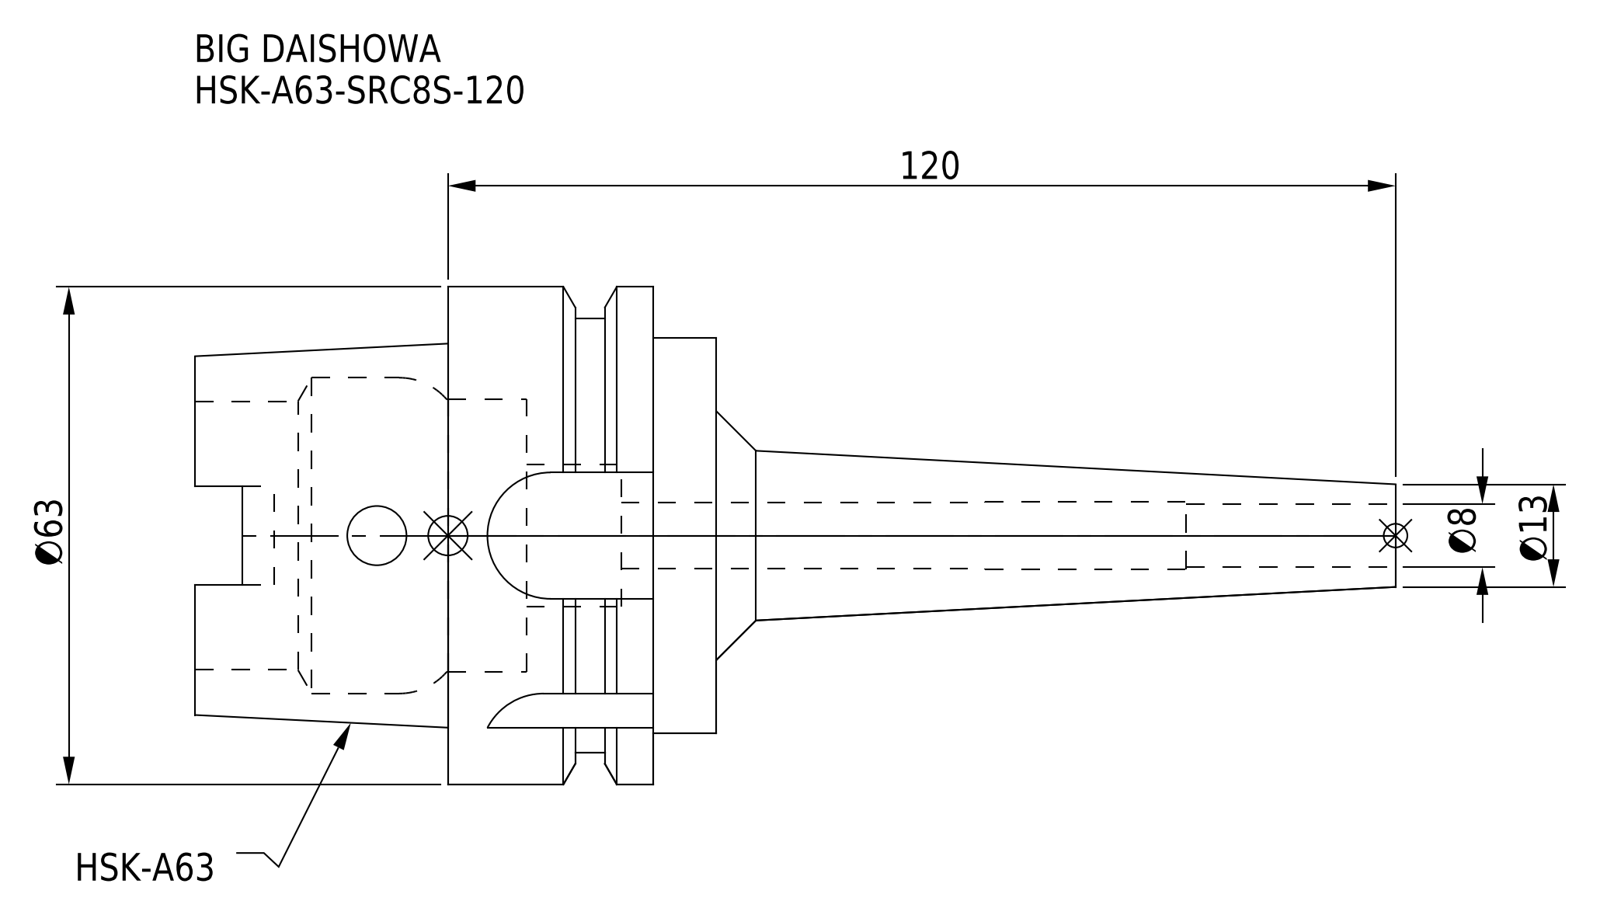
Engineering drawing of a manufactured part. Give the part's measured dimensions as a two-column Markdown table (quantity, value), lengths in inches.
| quantity | value |
| --- | --- |
| part name | HSK-A63-SRC8S-120 |
| STEP written by | CREO PARAMETRIC BY PTC INC, 2016380 (AUTOMOTIVE_DESIGN) |
| units | inches |
| bodies | 1 solid, 94 faces (39 planar, 37 cylindrical, 18 other) |
| overall size | 5.984 × 2.48 × 2.48 |
| volume | 6.974 in³ |
| surface area | 47.08 in² |
| round holes (diameter × count) | 0.295 × 1, 0.315 × 1, 0.331 × 1, 0.335 × 1, 0.709 × 1, 1.339 × 1, 1.358 × 1, 1.575 × 1 |
| round bosses / shafts (diameter × count) | 2.48 × 1, 2.165 × 1, 1.969 × 1 |
| partial cylindrical surfaces (radius × count) | 0.113 × 4, 0.315 × 4 |
| main face-to-face distances | 1.339, 1.024, 0.315, 0.947, 0.632, 0.392, 2.598, 2.283, 1.652, 1.26 |
